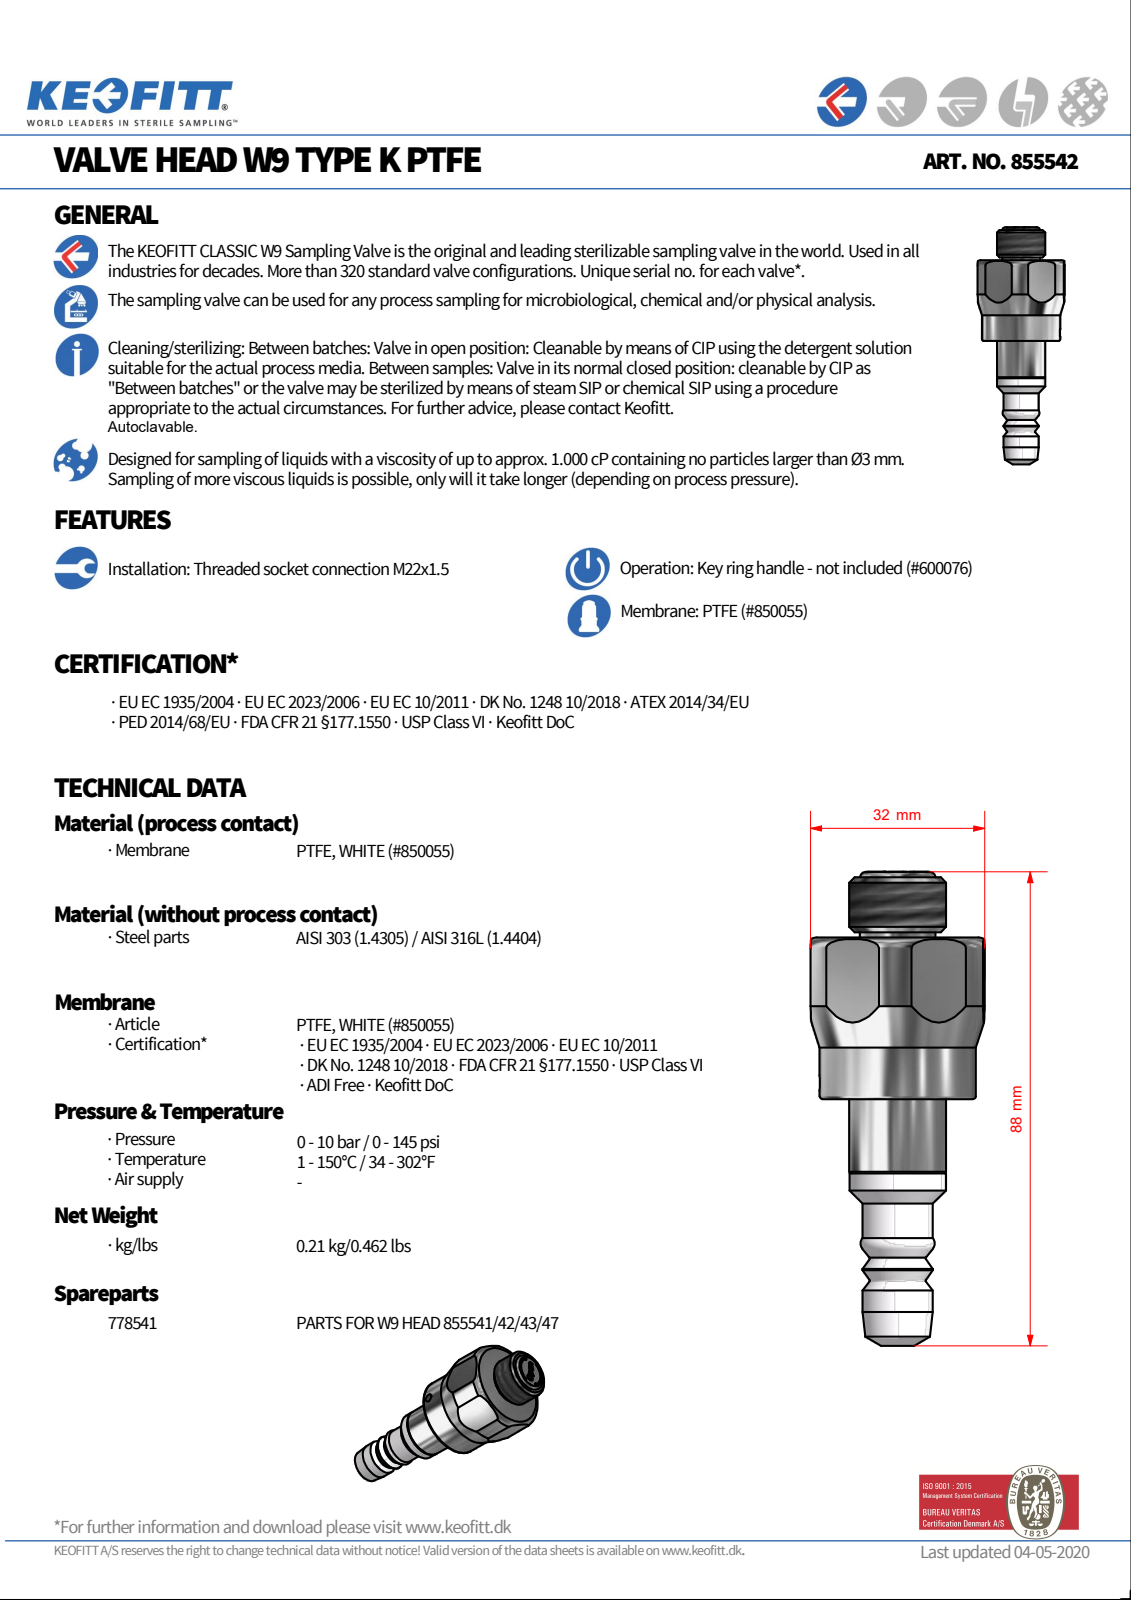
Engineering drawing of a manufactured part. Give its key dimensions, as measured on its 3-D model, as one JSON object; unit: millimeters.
{"step_written_by": "Autodesk Inventor 2008 (AUTOMOTIVE_DESIGN)", "units": "millimeters", "bodies": {"solids": 1, "faces": 158, "planar": 68, "cylindrical": 33, "other": 57}, "overall_size": [88, 34, 32.3], "volume_mm3": 33865, "surface_area_mm2": 7444, "round_holes": [[3.05, 1], [6.05, 1], [14, 1], [23.4, 1]], "round_bosses_or_shafts": [[29, 1], [18, 1], [17.9, 1], [17.52, 1], [13.8, 1], [13, 1], [3, 1]], "partial_cylinders_radius": [[1.5, 2], [5.15, 2], [5.55, 2], [1.75, 1], [13.52, 1], [17, 1]], "face_to_face_distances": [31.99, 30, 29.83, 32.01, 42.2, 42.03, 12.2, 1, 11.2, 31], "hole_center_spacings": [2]}
